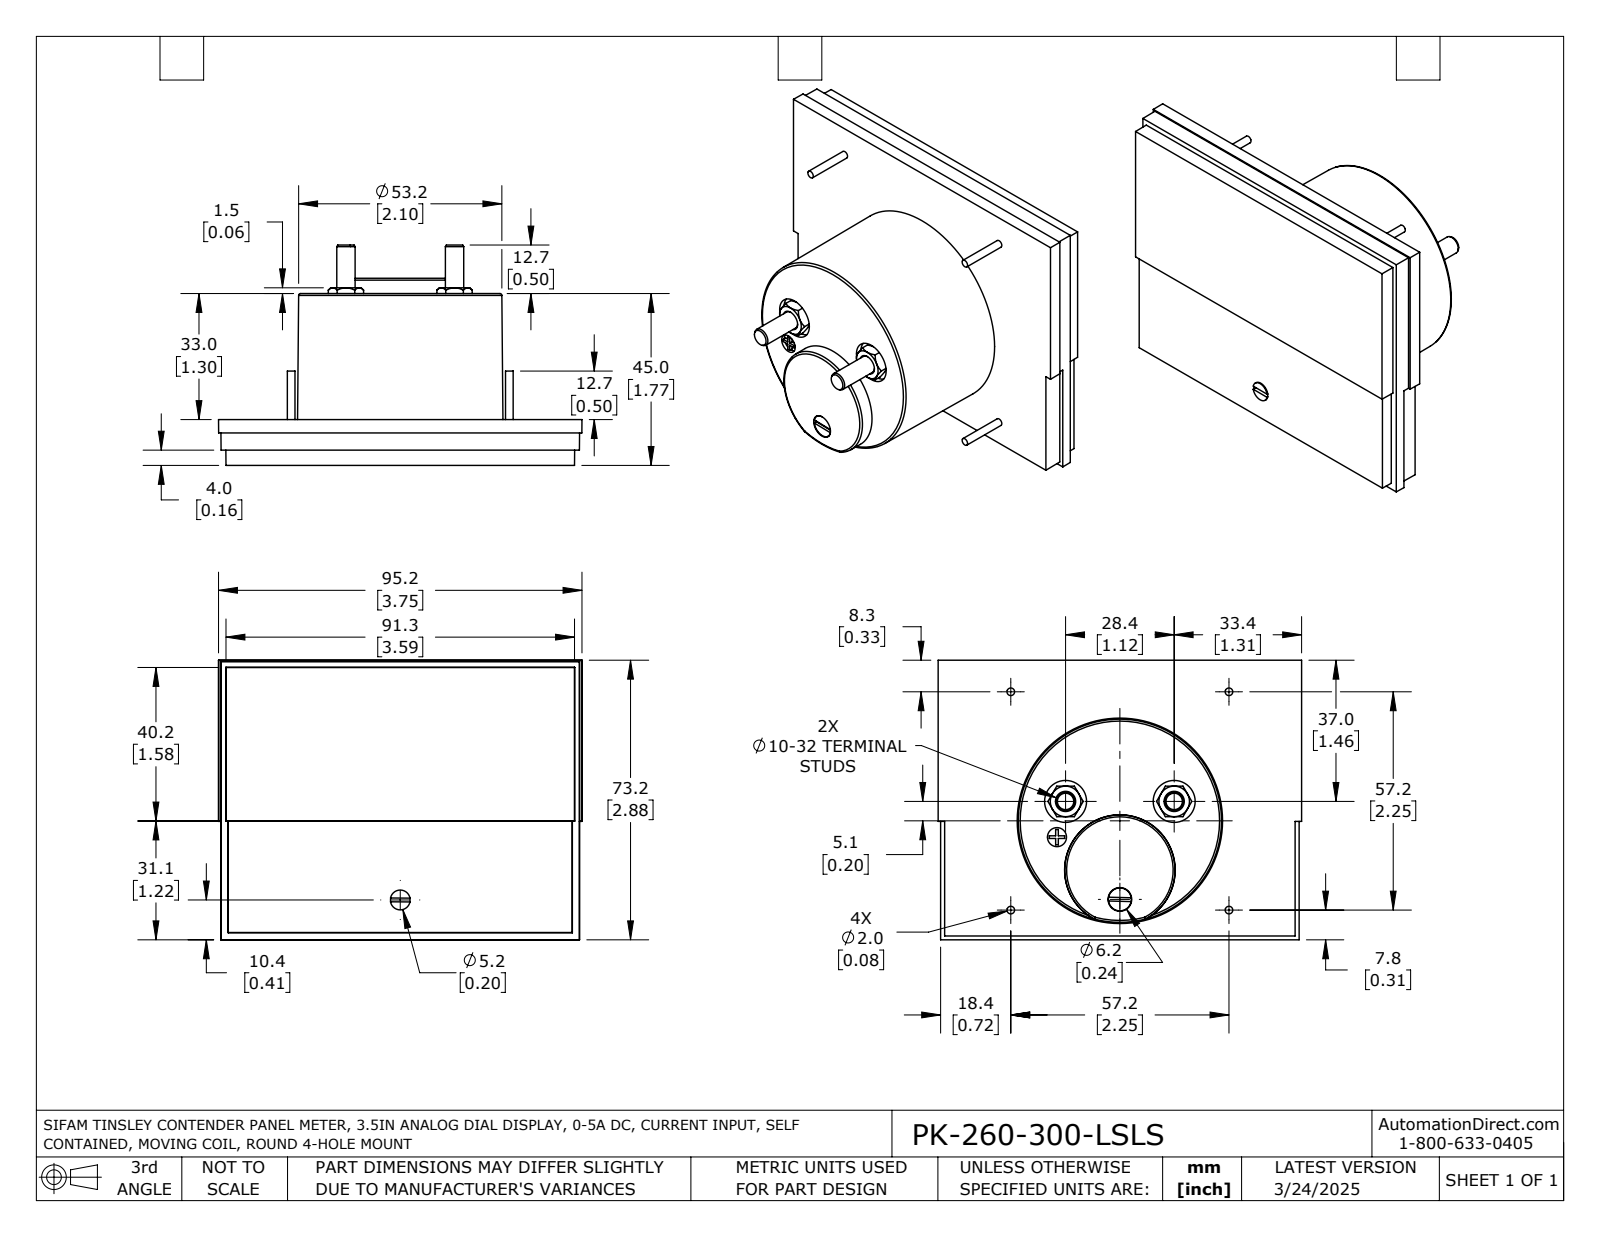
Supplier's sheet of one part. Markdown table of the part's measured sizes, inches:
| quantity | value |
| --- | --- |
| part name | PK-260-300-LSLS |
| STEP written by | SolidWorks 2021 (AUTOMOTIVE_DESIGN) |
| units | inches |
| bodies | 1 solid, 163 faces (76 planar, 31 cylindrical, 56 other) |
| overall size | 3.748 × 2.882 × 2.272 |
| volume | 9.446 in³ |
| surface area | 38.39 in² |
| round holes (diameter × count) | 0.433 × 2, 0.197 × 1, 0.244 × 1 |
| round bosses / shafts (diameter × count) | 0.079 × 4, 0.189 × 2, 0.236 × 1, 0.205 × 1 |
| partial cylindrical surfaces (radius × count) | 0.1 × 1 |
| main face-to-face distances | 0.472, 0.03, 0.443, 1.772, 1.299, 1.742, 0.157, 0.073, 0.315, 1.457 |
| hole center spacings | 1.155, 0.379, 0.912, 1.12, 1.263 |
